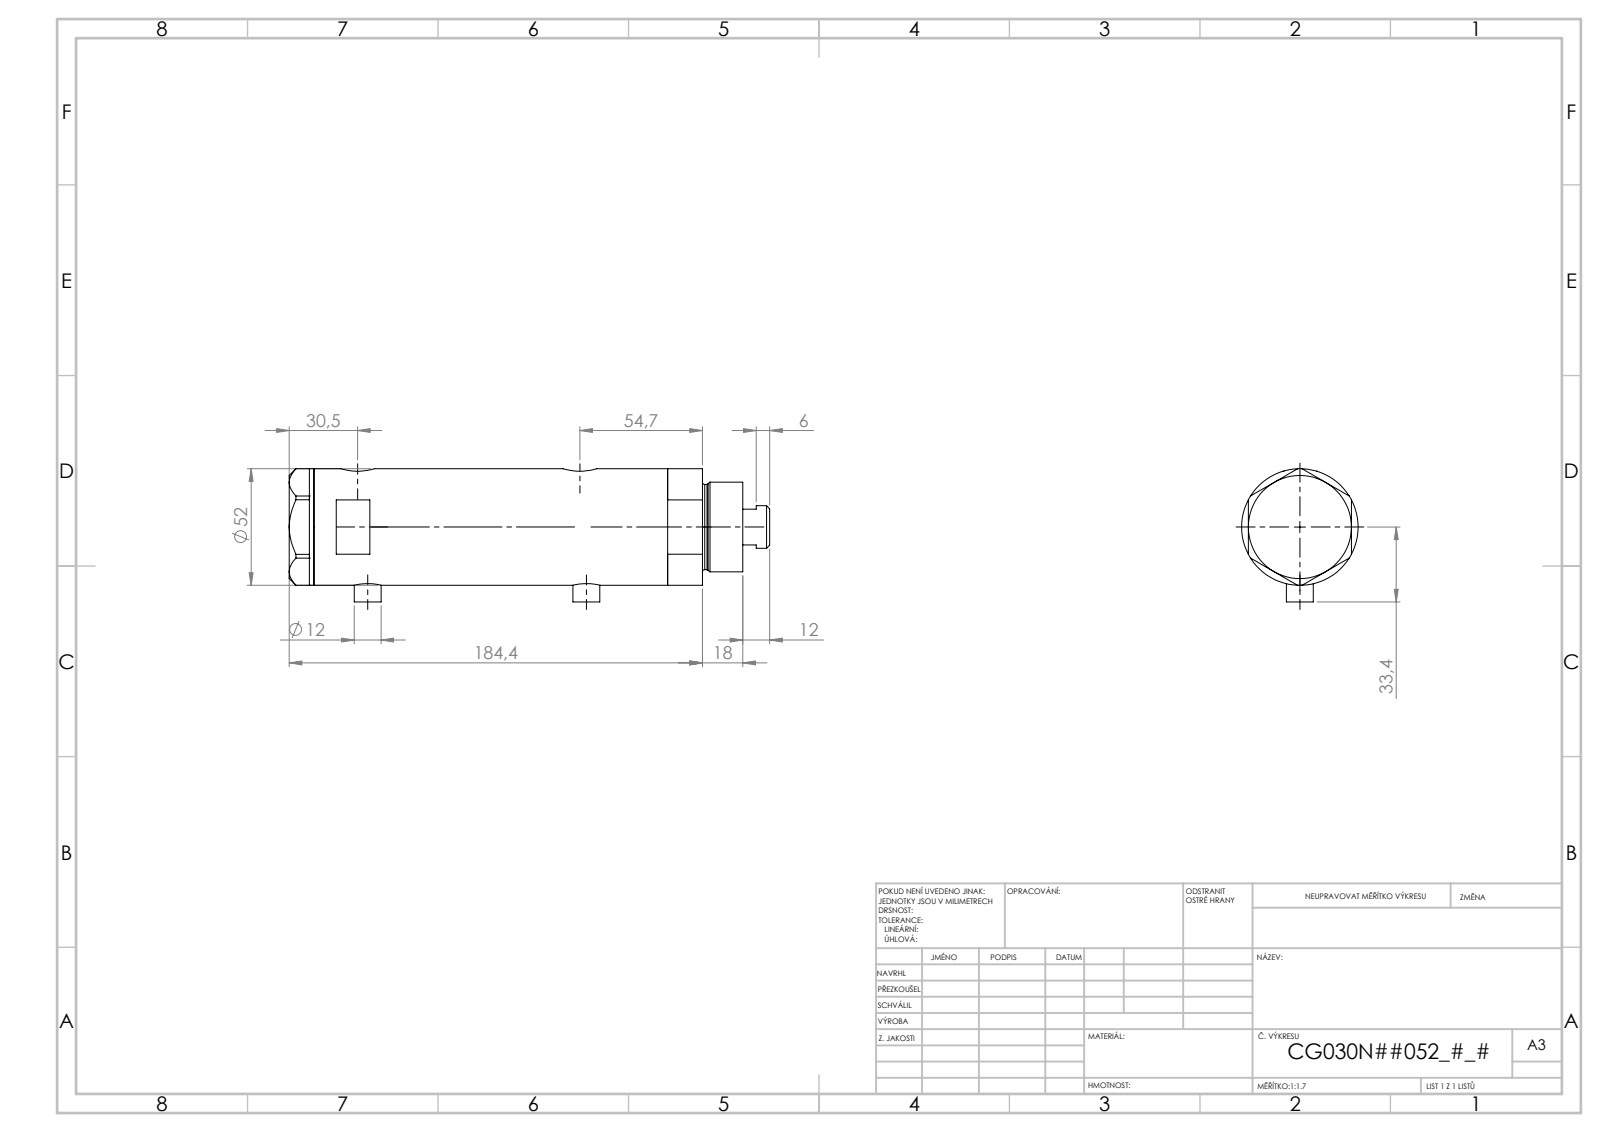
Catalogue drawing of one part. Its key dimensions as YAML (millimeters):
part_name: "V270CG_BACK; V270CG_FRONT; V270CG_VC; V270CG_MIDDLE"
step_written_by: "SolidWorks 2019 (CONFIG_CONTROL_DESIGN)"
units: millimeters
bodies: {solids: 4, faces: 140, planar: 67, cylindrical: 53, other: 20}
overall_size: [201.02, 53.1, 52]
volume: 357532
surface_area: 81752
round_holes:
  - {diameter: 5, count: 2}
  - {diameter: 9.73, count: 2}
  - {diameter: 12.5, count: 2}
  - {diameter: 15, count: 2}
  - {diameter: 6.5, count: 1}
  - {diameter: 20, count: 1}
  - {diameter: 21.5, count: 1}
  - {diameter: 30, count: 1}
  - {diameter: 33, count: 1}
  - {diameter: 44, count: 1}
round_bosses_or_shafts:
  - {diameter: 12, count: 2}
  - {diameter: 52, count: 1}
  - {diameter: 40, count: 1}
  - {diameter: 38, count: 1}
  - {diameter: 19, count: 1}
face_to_face_distances: [105.54, 23.8, 81.74, 11, 34.8, 116.54, 46, 152.94, 141.94, 118.14]
hole_center_spacings: [2.9, 4.5, 78.75, 81.65, 83.25, 86.15, 2.89, 2.91]
